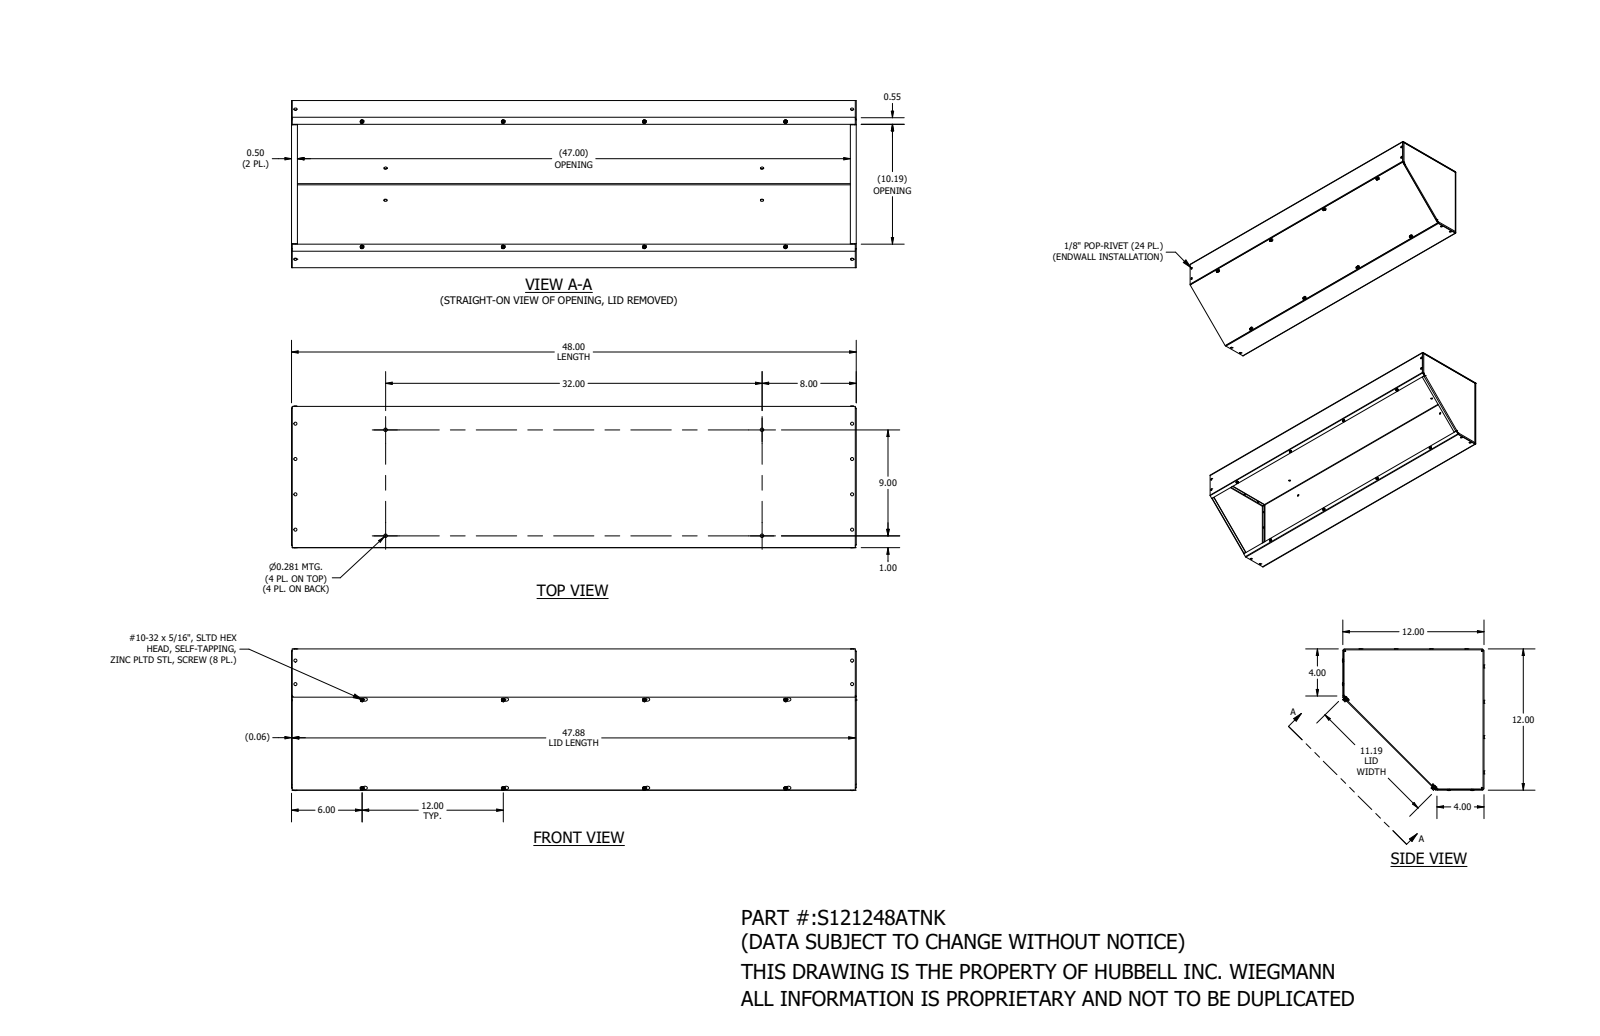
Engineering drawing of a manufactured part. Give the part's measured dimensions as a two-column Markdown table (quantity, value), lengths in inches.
| quantity | value |
| --- | --- |
| part name | S121248ATNK |
| STEP written by | SolidWorks 2021 (AUTOMOTIVE_DESIGN) |
| units | inches |
| bodies | 36 solids, 1806 faces (416 planar, 510 cylindrical, 880 other) |
| overall size | 48 × 12.08 × 12.08 |
| volume | 174 in³ |
| surface area | 4 738 in² |
| round holes (diameter × count) | 0.129 × 24, 0.171 × 8, 0.281 × 8, 0.406 × 8 |
| round bosses / shafts (diameter × count) | 0.262 × 24, 0.125 × 18, 0.313 × 8, 0.181 × 8, 0.125 × 6 |
| partial cylindrical surfaces (radius × count) | 0.064 × 48, 0.136 × 15, 0.062 × 9, 0.109 × 8, 0.063 × 6 |
| main face-to-face distances | 0.074, 11.926, 11.852, 12, 47.926, 48, 47.852, 0.067, 0.141, 0.148 |
| hole center spacings | 3, 12, 47.313, 47.407, 1.5, 6, 7.674, 9 |
